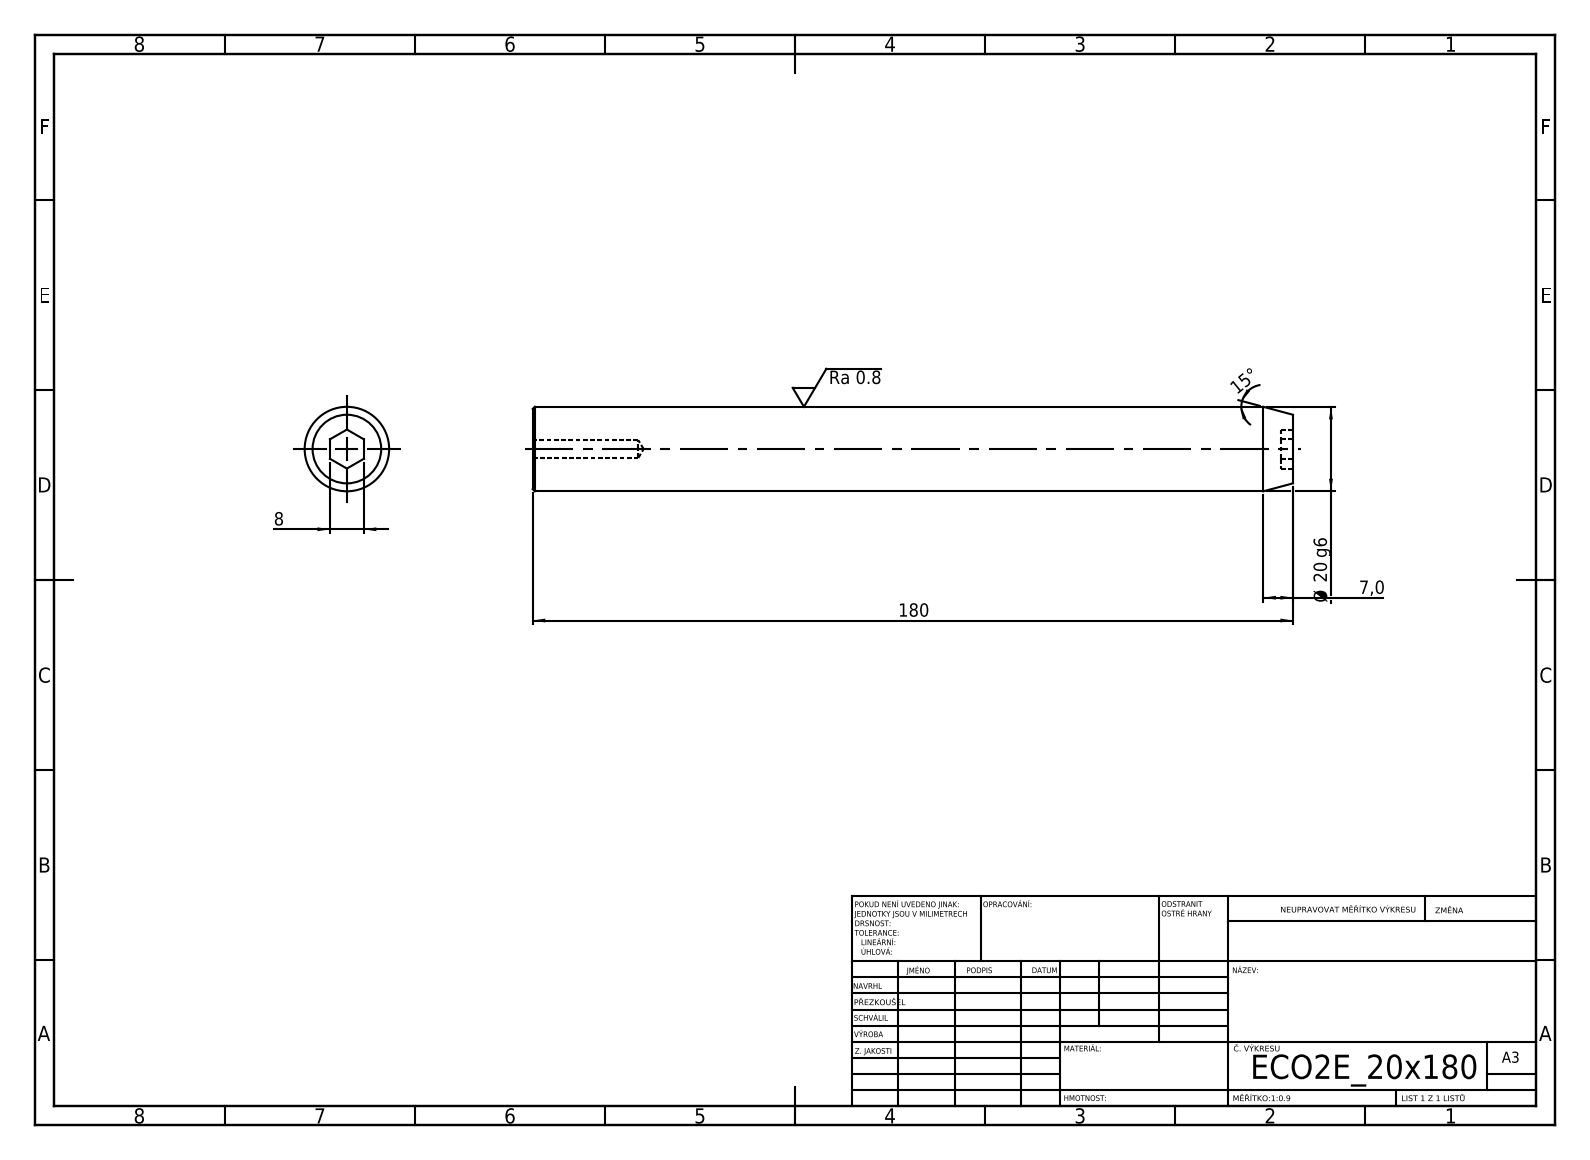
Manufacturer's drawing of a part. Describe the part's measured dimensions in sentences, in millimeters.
Its 3-D file was written by "SolidWorks 2019 (CONFIG_CONTROL_DESIGN)". It is 1 solid with 19 faces: 9 planar, 4 cylindrical and 6 other. Overall it measures 180 by 20 by 20 millimeters. Its volume is 55 647 cubic millimeters and its surface area 12 195 square millimeters. Round holes: 1 of diameter 4.2. Round bosses or shafts: 1 of diameter 20. The main face-to-face distances are 180, 2.8, 177.2, 8.
